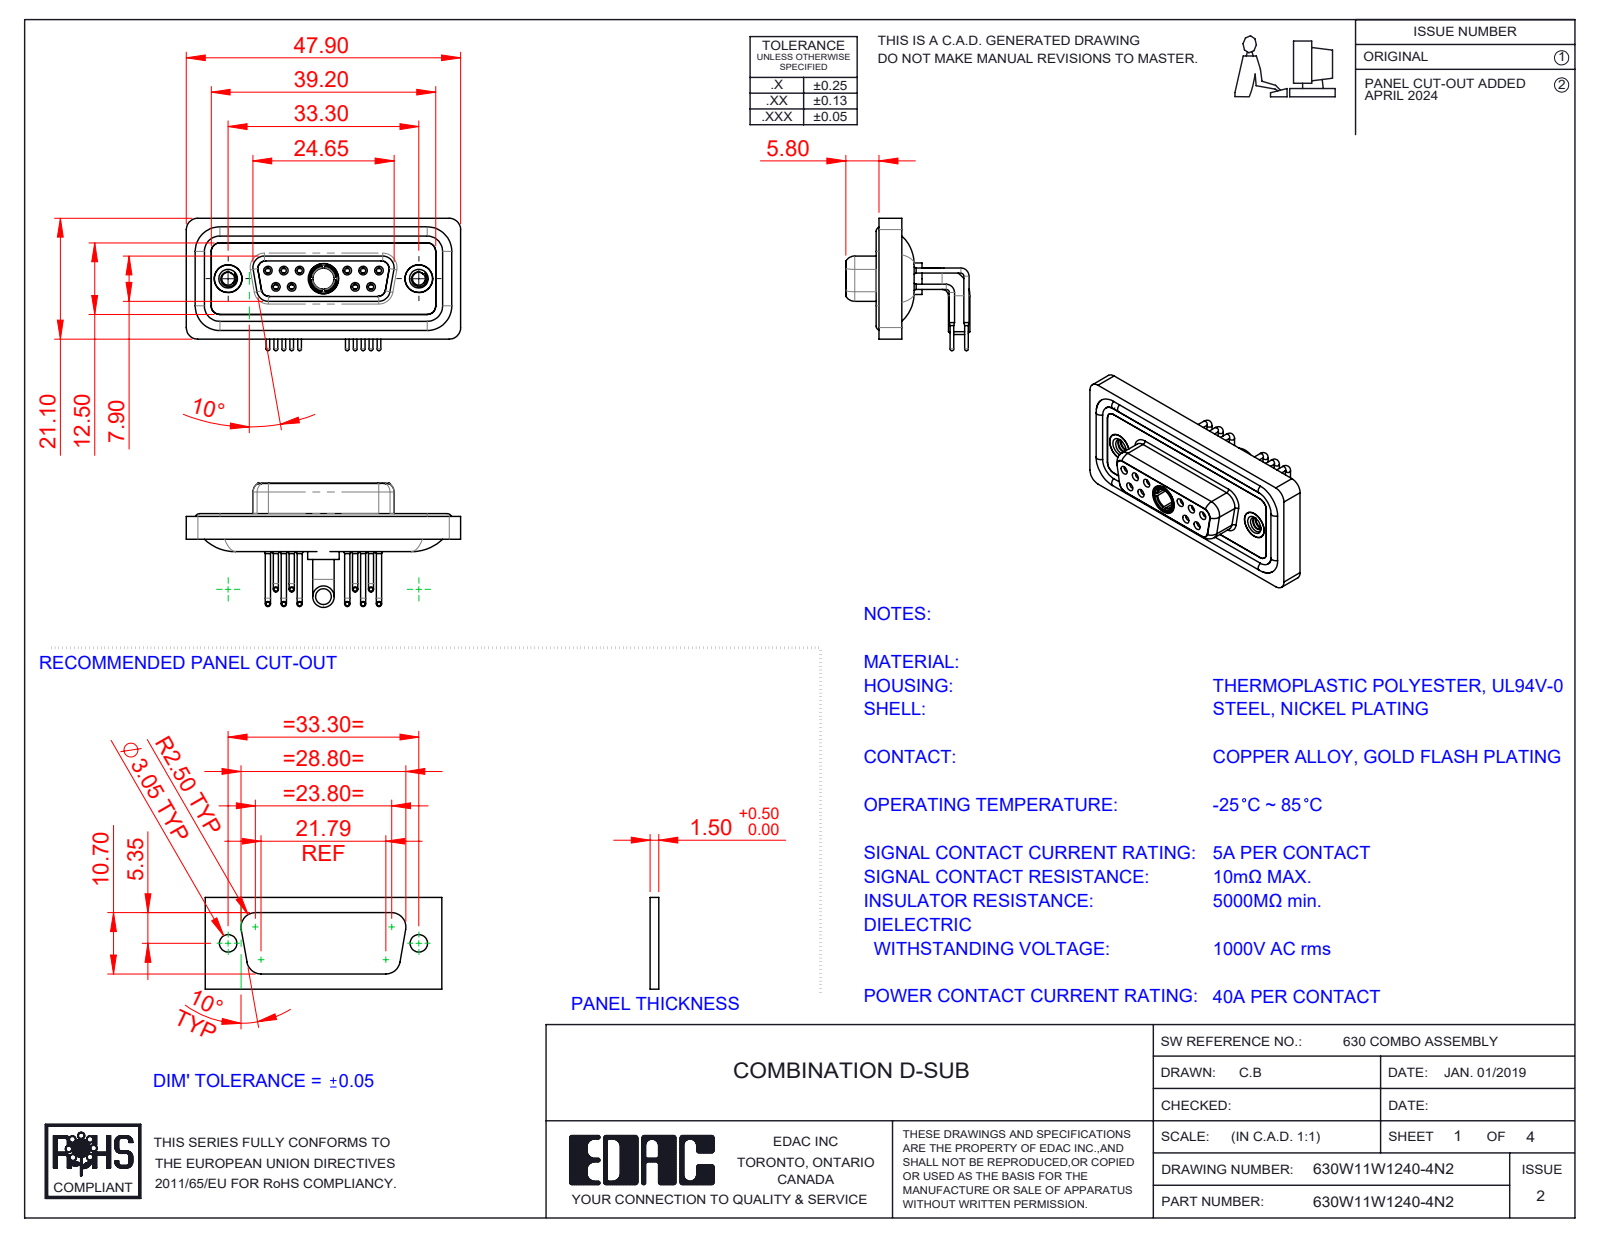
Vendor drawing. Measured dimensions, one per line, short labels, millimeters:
name: 630W11W1140-4N2; 630Combo Waterproof Housing_15 Contacts; 630Combo Contact Row 2_50 Contacts; 630Combo Threaded Rivet_2 (+5 more)
written by: SolidWorks 2020 (CONFIG_CONTROL_DESIGN)
unit: mm
bodies: 19 solids, 994 faces (284 planar, 443 cylindrical, 267 other)
size: 47.9 × 23.12 × 21.68
volume: 6 290 mm³; area: 10 514 mm²
holes: 10× ⌀0.9, 10× ⌀1.1, 10× ⌀1.5, 10× ⌀2, 6× ⌀1.7, 4× ⌀1.6, 3× ⌀4.85, 2× ⌀2.26, 2× ⌀4, 2× ⌀4.05, 2× ⌀5, 1× ⌀3.7
bosses: 10× ⌀1.6, 10× ⌀0.9, 10× ⌀0.65, 2× ⌀4.95, 2× ⌀4.8, 2× ⌀3.75, 1× ⌀5.5, 1× ⌀5.2
rounds: 20× R2, 18× R1.5, 12× R1.35, 8× R1.6, 4× R0.25, 4× R0.5, 4× R0.6, 4× R0.65
face distances: 0.4, 1.8, 1.1, 1.6, 2.5, 2.9, 3.1, 3.7, 4.1, 1.5
hole spacings: 3.16, 2.77, 13.85, 11.08, 16.62, 5.03, 5.04, 5.54
